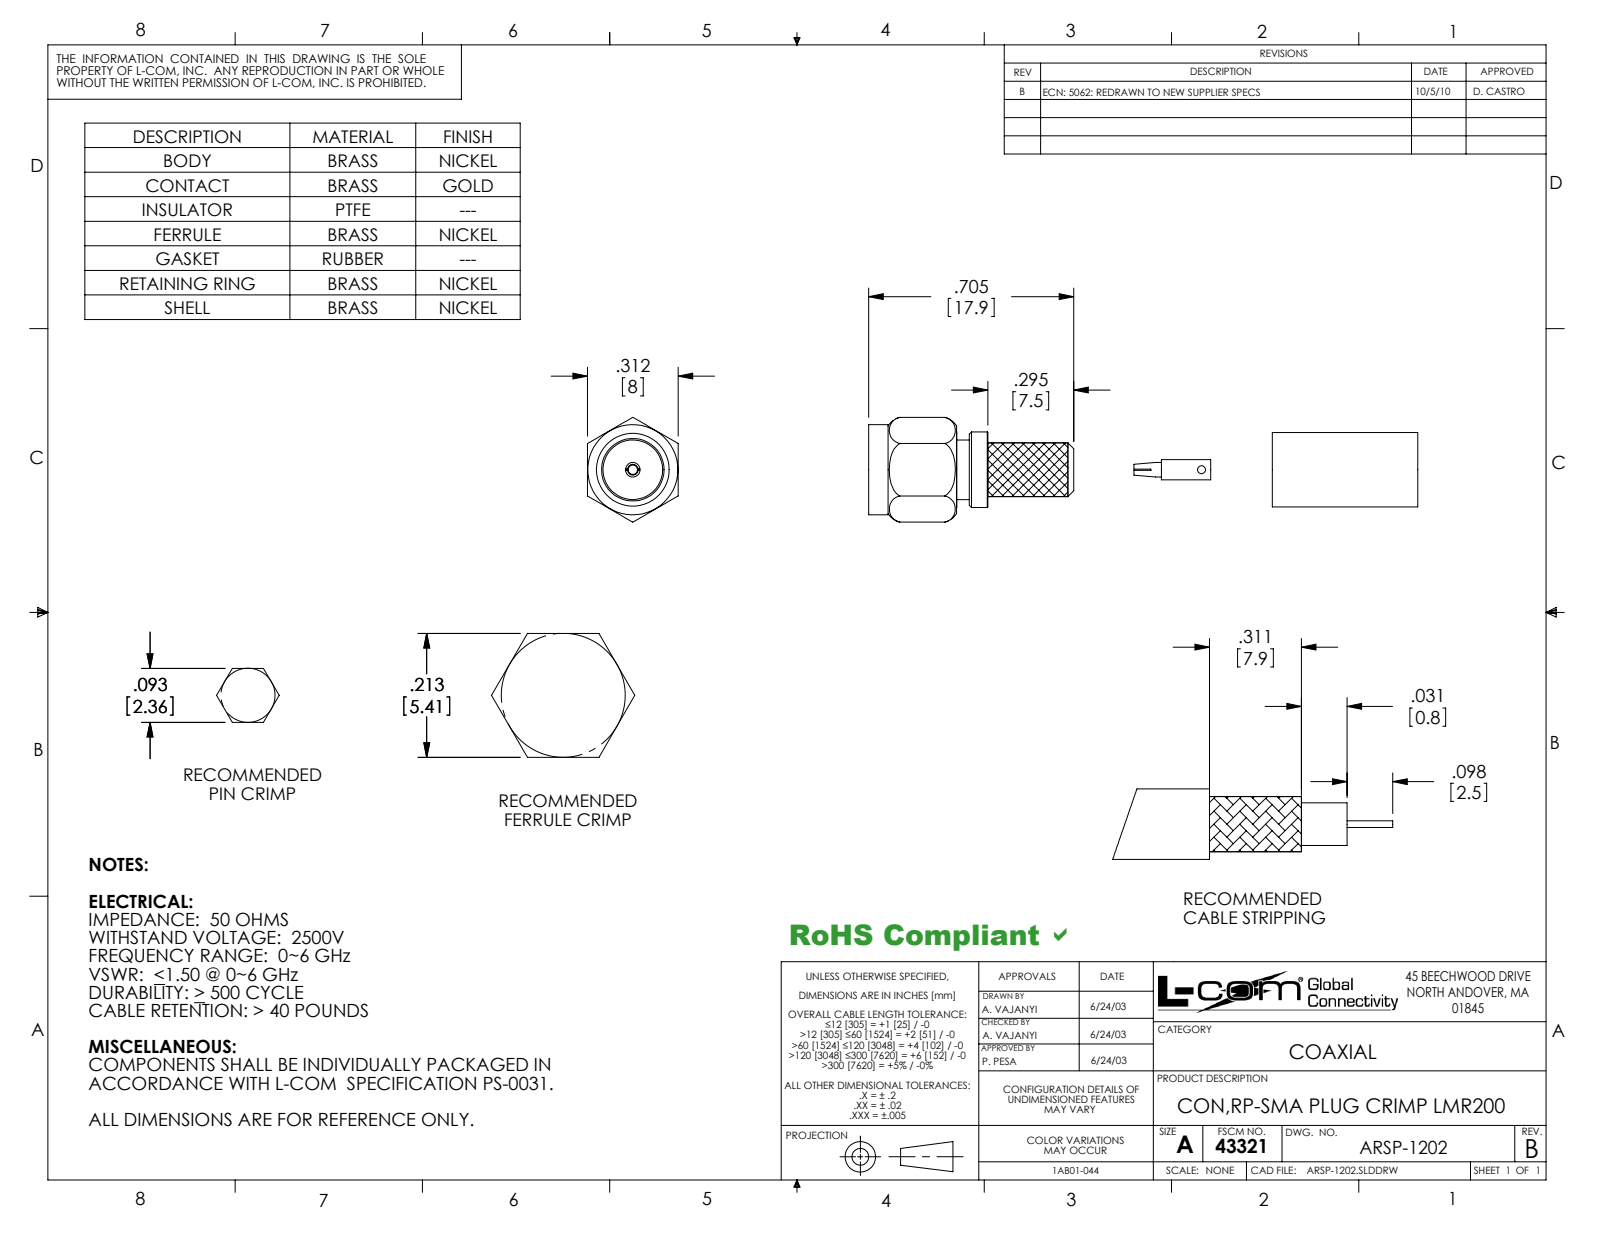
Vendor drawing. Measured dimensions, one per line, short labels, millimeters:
name: ARSP-1202-MA2; ARSP-1202-MA1; ARSP-1202; ARSP-1202-MA3
written by: SolidWorks 2010 (CONFIG_CONTROL_DESIGN)
unit: mm
bodies: 3 solids, 79 faces (31 planar, 34 cylindrical, 14 other)
size: 48 × 9.1 × 7.9
volume: 570 mm³; area: 1 343 mm²
holes: 1× ⌀0.7, 1× ⌀1.2, 1× ⌀1.3, 1× ⌀1.6, 1× ⌀5.2, 1× ⌀5.5, 1× ⌀6.4
bosses: 1× ⌀7.9, 1× ⌀6.6, 1× ⌀6.5, 1× ⌀5.5, 1× ⌀5.2, 1× ⌀4.7, 1× ⌀1.8
face distances: 7.9, 4.5, 7.7, 3.2, 2.7, 7.2, 10.4, 4.5, 2.7, 7.7
